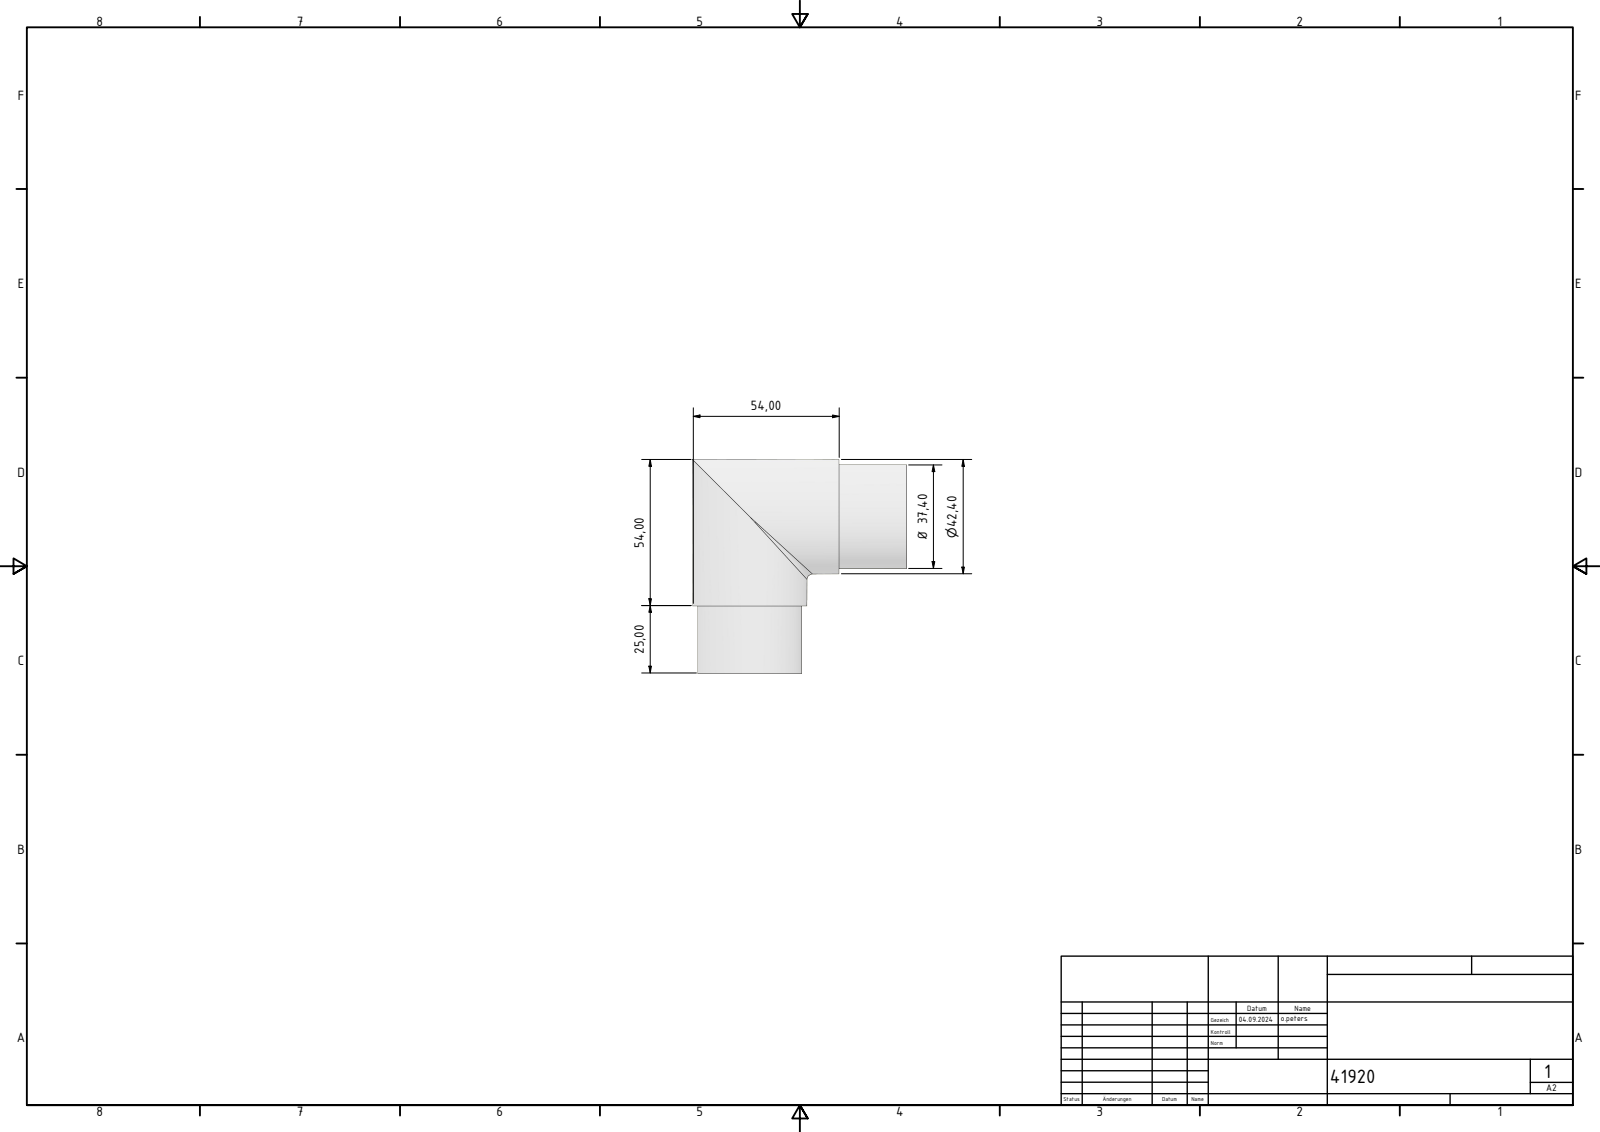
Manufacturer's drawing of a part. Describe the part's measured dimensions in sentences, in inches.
The part is named "41920". Its 3-D file was written by "Autodesk Inventor 2022 (AUTOMOTIVE_DESIGN)". It is 1 solid with 14 faces: 6 planar, 8 cylindrical and 0 other. Overall it measures 3.11 by 3.11 by 1.669 inches. Its volume is 1.764 cubic inches and its surface area 45.49 square inches. Round holes: 2 of diameter 1.315, 2 of diameter 1.512. Round bosses or shafts: 2 of diameter 1.669, 2 of diameter 1.472. The main face-to-face distances are 0.079, 0.984, 1.063.
